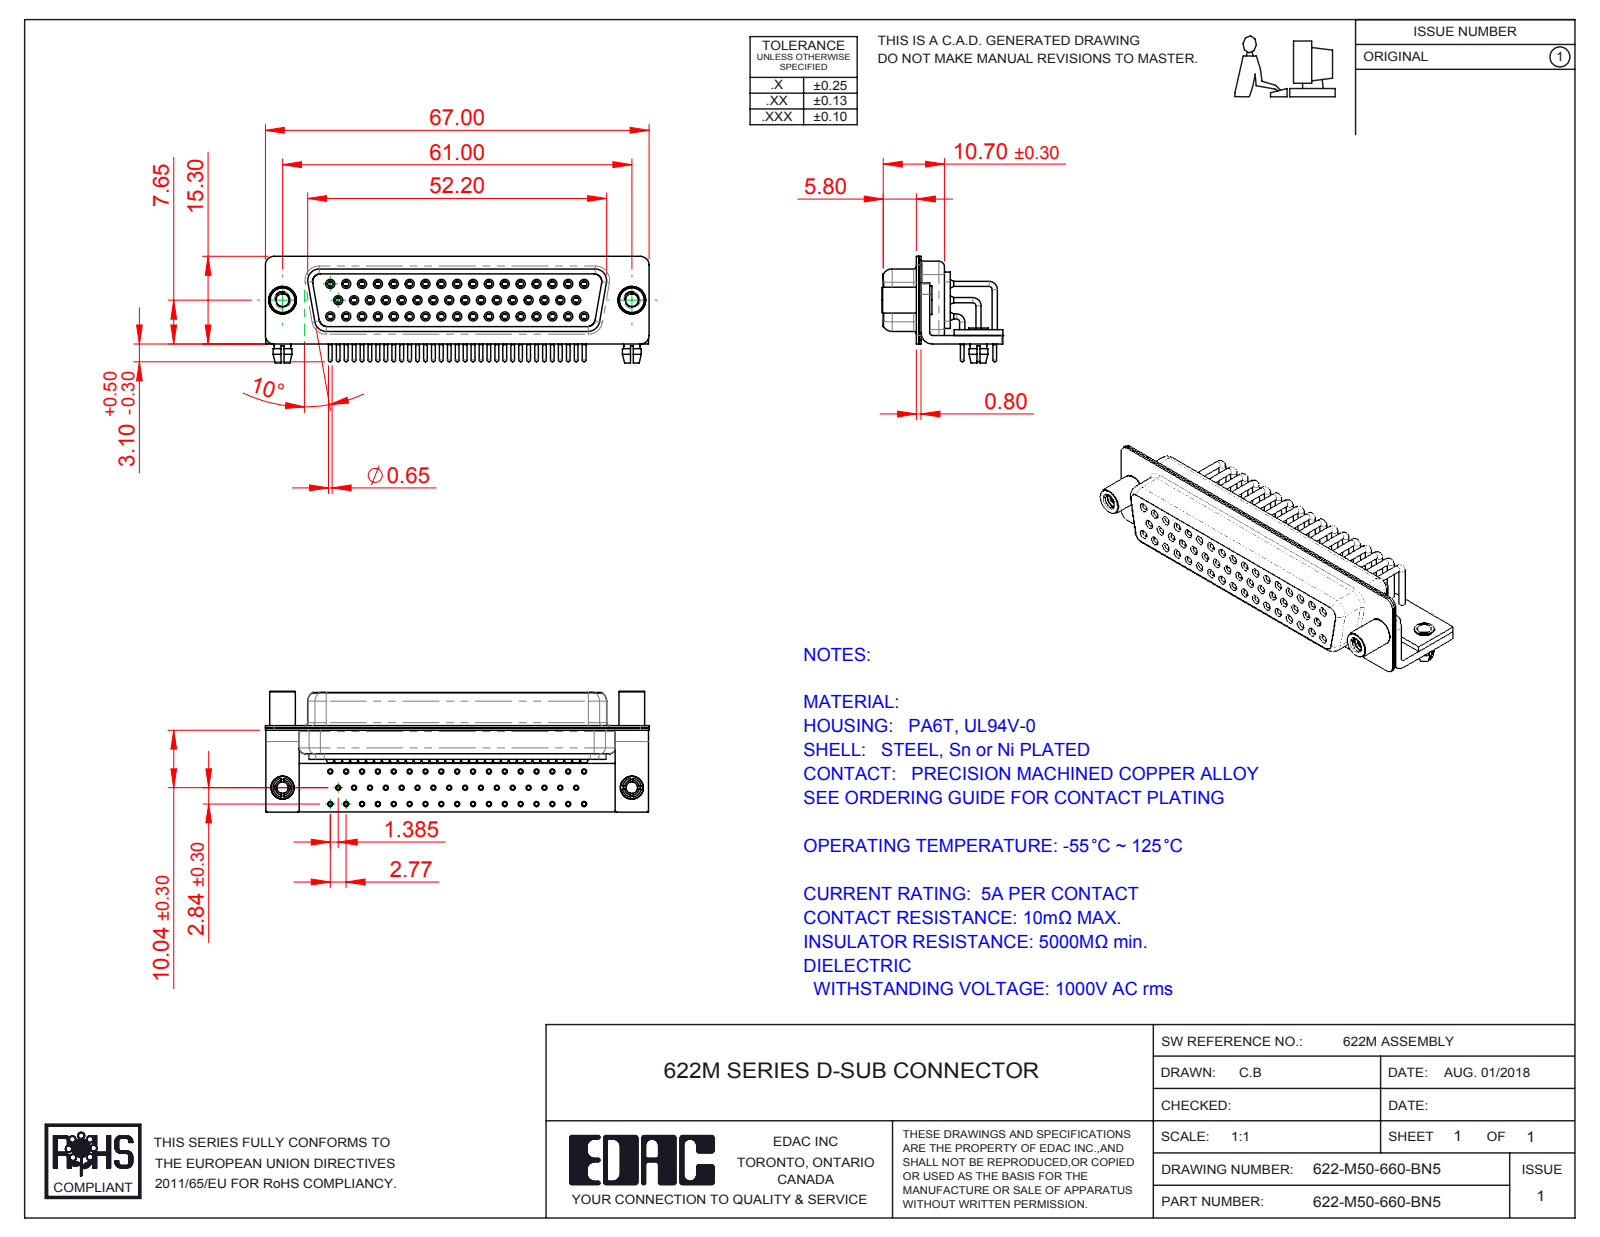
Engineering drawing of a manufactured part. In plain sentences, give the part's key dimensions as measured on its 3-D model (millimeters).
The part is named "622M Shell Rear_50 Contacts; 622-M50-660-BN5; 622M Contact Row 3; 622M Shell Front_50 Contacts (+7 more)". Its 3-D file was written by "SolidWorks 2016 (CONFIG_CONTROL_DESIGN)". It is 60 solids with 3221 faces: 893 planar, 1483 cylindrical and 845 other. Overall it measures 67 by 21.1 by 18.6 millimeters. Its volume is 7 917 cubic millimeters and its surface area 18 677 square millimeters. Round holes: 52 of diameter 2, 50 of diameter 0.9, 50 of diameter 1, 50 of diameter 1.1, 50 of diameter 1.7, 50 of diameter 1.8, 2 of diameter 2.26, 2 of diameter 2.5, 2 of diameter 3.2, 2 of diameter 4, 2 of diameter 4.8. Round bosses or shafts: 59 of diameter 0.9, 50 of diameter 1.6, 50 of diameter 1.5, 50 of diameter 0.65, 2 of diameter 5, 2 of diameter 4.9, 2 of diameter 4.5, 2 of diameter 4. Partial cylindrical surfaces (rounded edges, fillets, slot ends): 16 of radius 0.25, 16 of radius 1.5, 13 of radius 2, 8 of radius 1.35, 8 of radius 1.6, 5 of radius 0.5, 4 of radius 0.6, 4 of radius 0.65. The main face-to-face distances are 0.4, 1, 2.2, 0.85, 1.35, 11.85, 12.25, 5.8, 0.8, 5.9. The hole center spacings are 2.77, 3.16, 5.54, 8.31, 11.08, 13.85, 16.62, 19.39.
